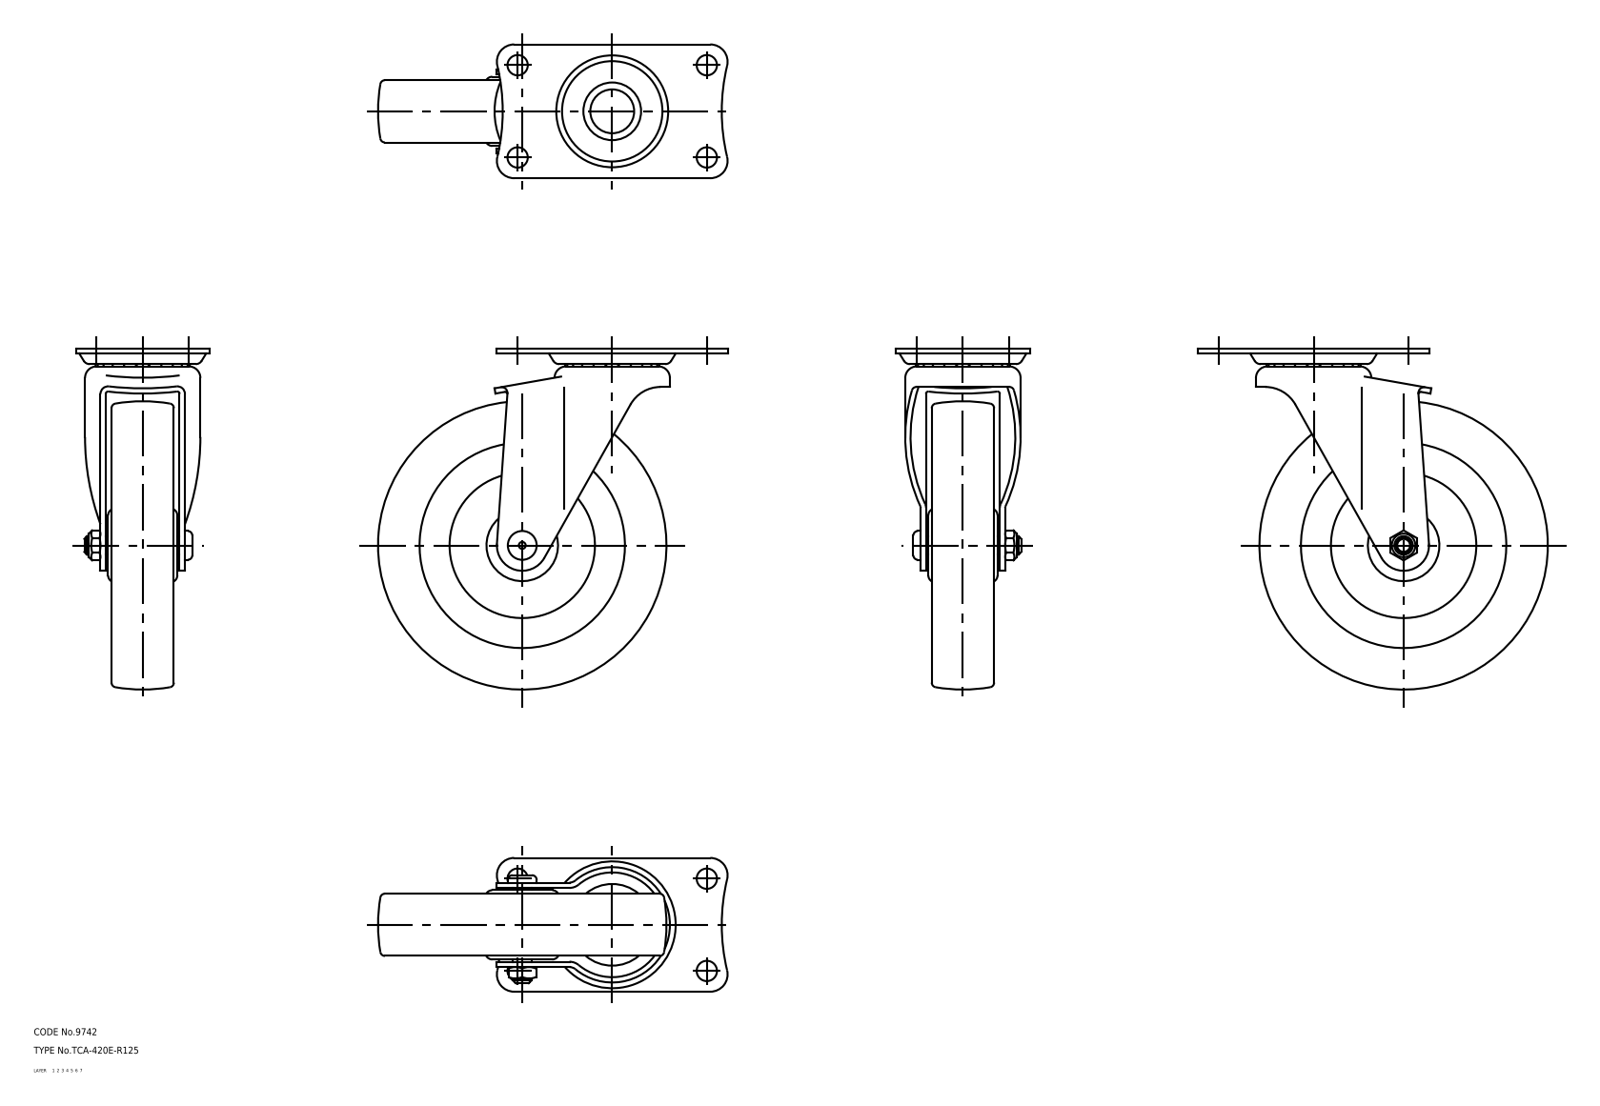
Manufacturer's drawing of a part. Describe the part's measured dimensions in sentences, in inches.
The part is named "wheel; mounting plate; main shaft; axle (+1 more)". Its 3-D file was written by "CADfix (AUTOMOTIVE_DESIGN)". It is 5 solids with 228 faces: 0 planar, 0 cylindrical and 228 other. Overall it measures 5.965 by 5.827 by 2.283 inches. Its volume is 22.23 cubic inches and its surface area 114.3 square inches.
